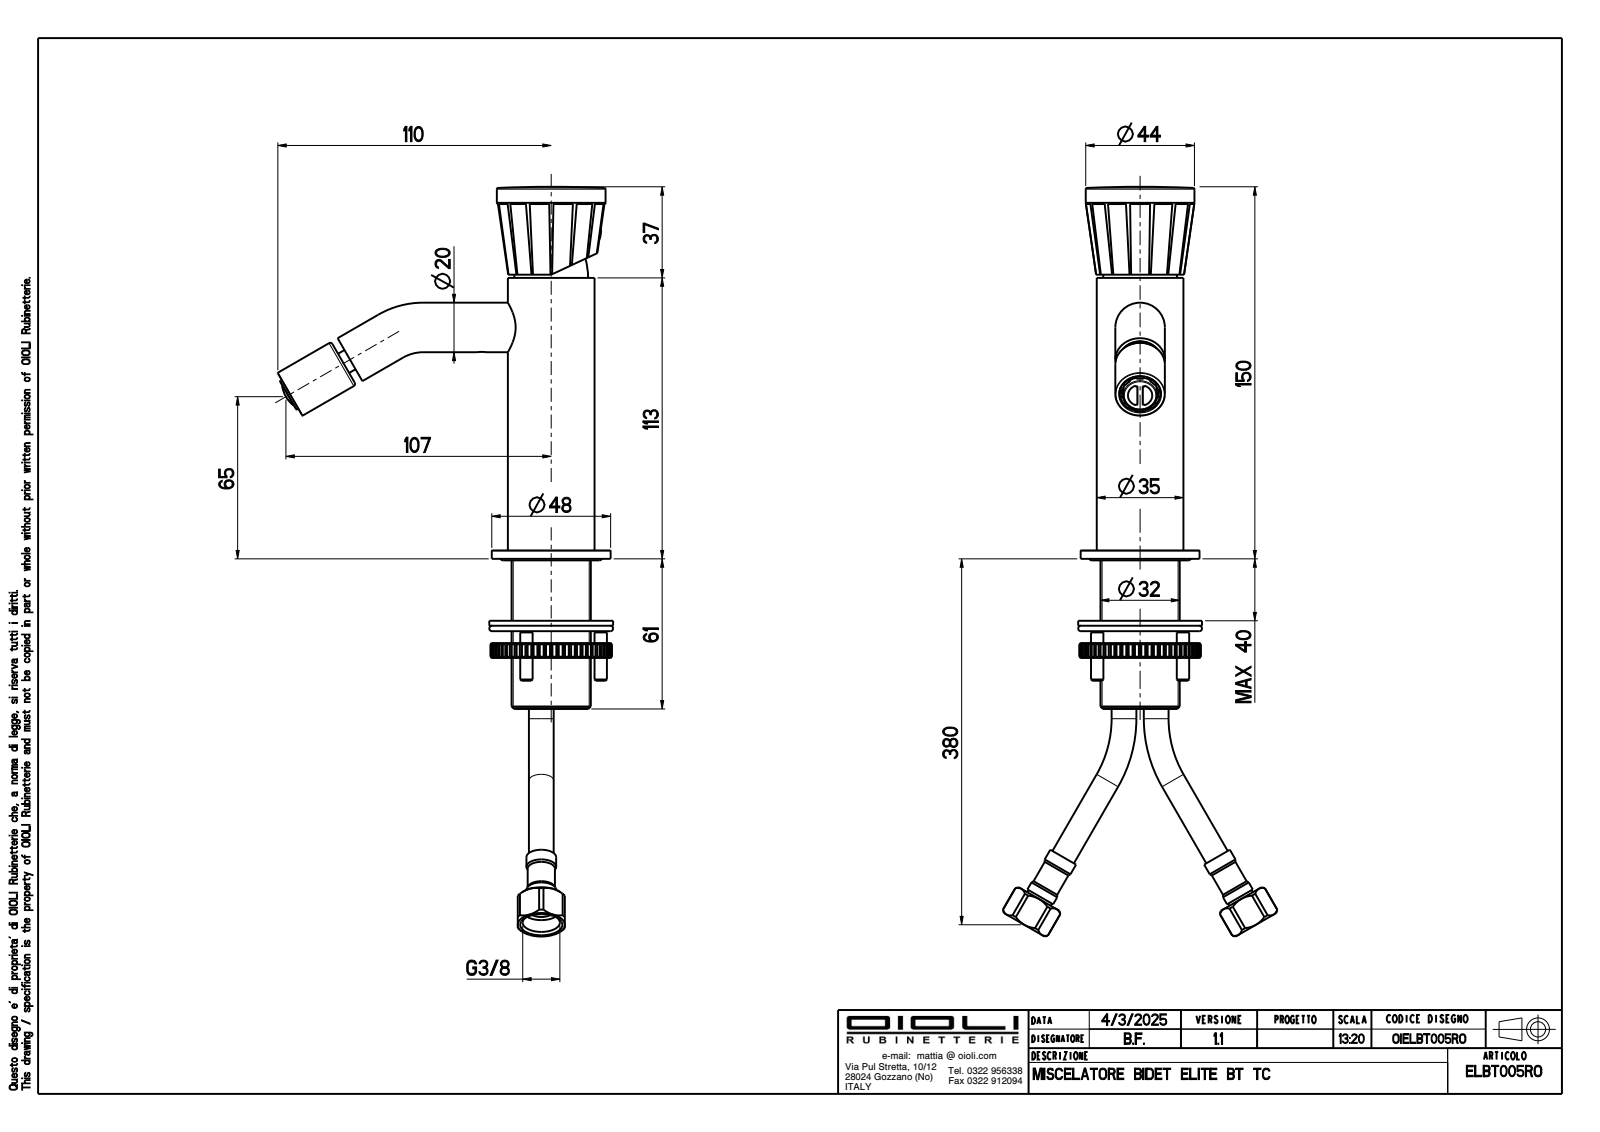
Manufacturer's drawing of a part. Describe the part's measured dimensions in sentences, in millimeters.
The part is named "OIBR00322; OIBR00066; OICT00093; OIVT00002 (+7 more)". Its 3-D file was written by "CREO PARAMETRIC BY PTC INC, 2024493 (CONFIG_CONTROL_DESIGN)". It is 11 solids with 1057 faces: 591 planar, 208 cylindrical and 258 other. Overall it measures 150.18 by 134.42 by 48 millimeters. Its volume is 83 960 cubic millimeters and its surface area 55 754 square millimeters. Round holes: 2 of diameter 3.2, 2 of diameter 5, 2 of diameter 7, 2 of diameter 9, 2 of diameter 15.5, 1 of diameter 3.3, 1 of diameter 4, 1 of diameter 4.2, 1 of diameter 5.3, 1 of diameter 6.5, 1 of diameter 9.5, 1 of diameter 11. Round bosses or shafts: 2 of diameter 20, 2 of diameter 16.5, 2 of diameter 8, 1 of diameter 48, 1 of diameter 43.9, 1 of diameter 35.6, 1 of diameter 35, 1 of diameter 32. Partial cylindrical surfaces (rounded edges, fillets, slot ends): 14 of radius 0.1, 8 of radius 0.9, 6 of radius 0.6, 3 of radius 0.45, 1 of radius 2.5, 1 of radius 3.25, 1 of radius 6.72, 1 of radius 7.46. The main face-to-face distances are 143.8, 3.4, 147.2, 63.4, 60, 83.8, 28, 113.4, 110, 50. The hole center spacings are 1.9, 6.72, 7.63, 8.14, 8.94, 9.33, 11.27, 15.46.
